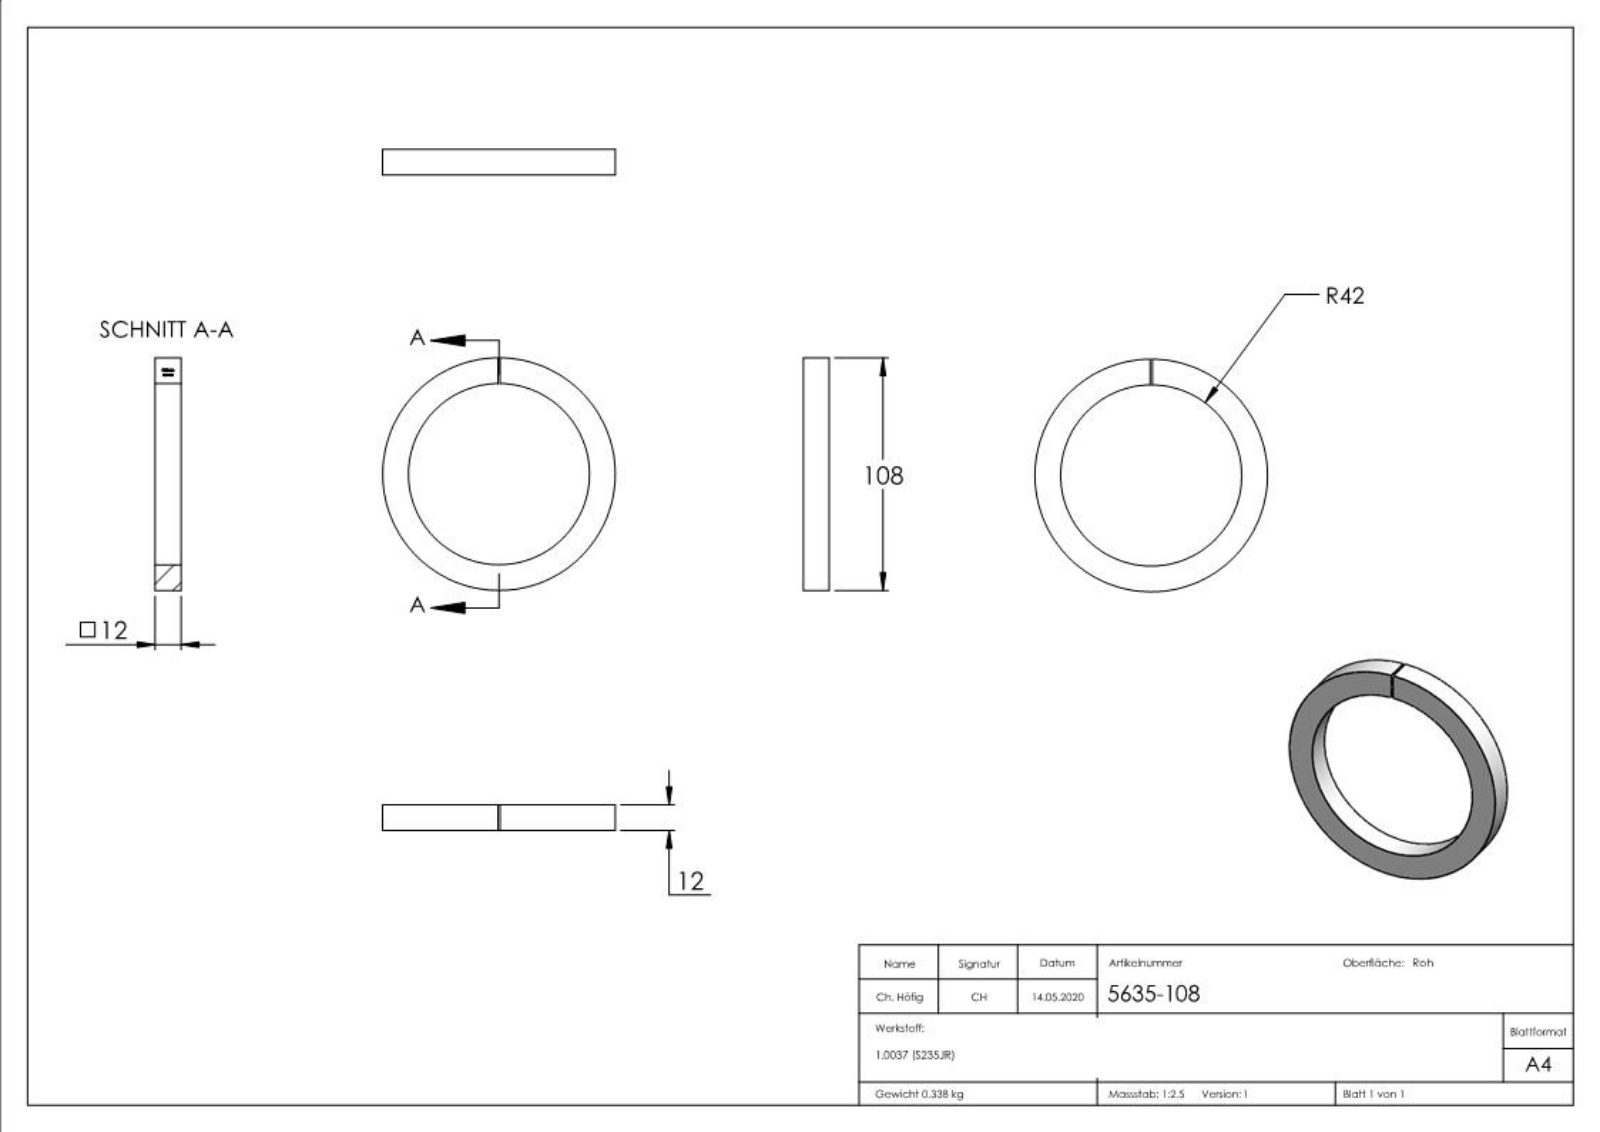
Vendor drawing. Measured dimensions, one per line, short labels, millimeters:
name: 5635-108
written by: SolidWorks 2015 (CONFIG_CONTROL_DESIGN)
unit: mm
bodies: 1 solid, 224 faces (109 planar, 2 cylindrical, 113 other)
size: 108 × 108 × 12
volume: 43 285 mm³; area: 14 722 mm²
holes: 1× ⌀84
bosses: 1× ⌀108
face distances: 12, 1, 1.1, 1.78, 0.83, 2.12, 0.99, 2.77, 1.21, 3.33
